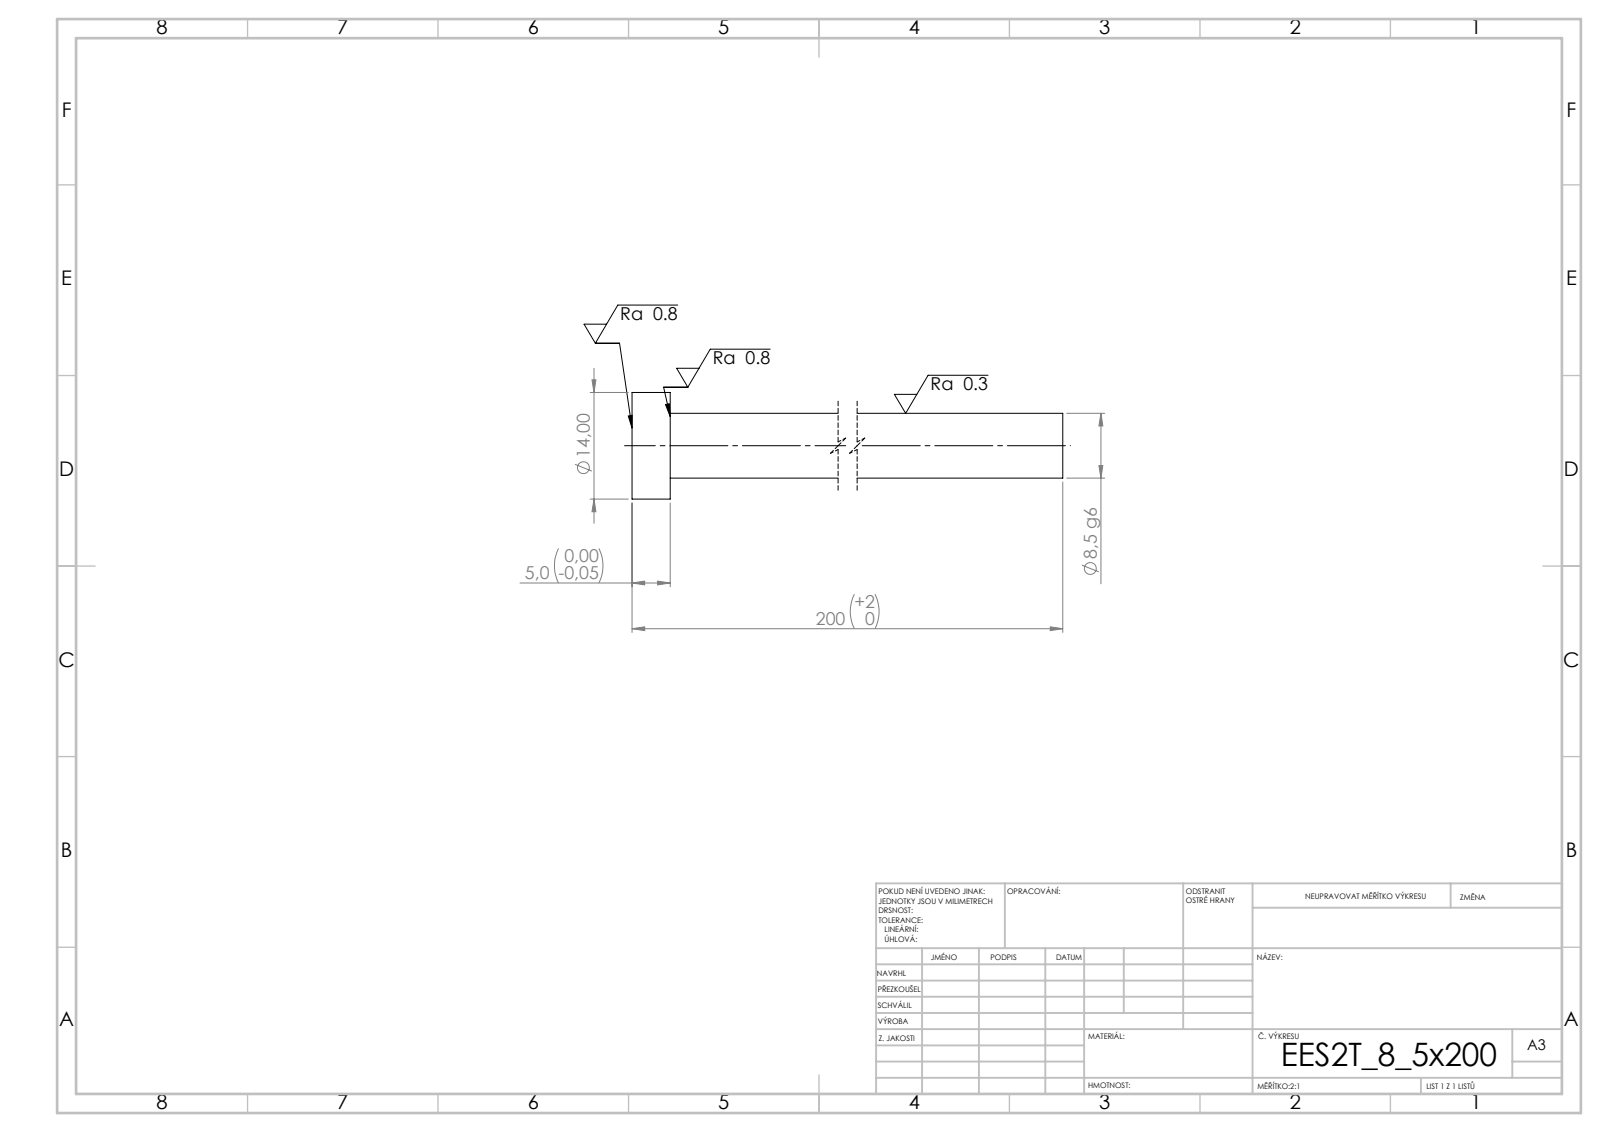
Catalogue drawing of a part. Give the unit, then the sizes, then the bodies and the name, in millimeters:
Units: millimetres
Overall size (bounding box): 200 × 14 × 14
Round bosses / shafts (diameter × count): ⌀14 ×1, ⌀8.5 ×1
Main face-to-face distances: 5, 200, 195
Volume: 11 835 mm³ · Surface area: 5 735 mm²
Bodies: 1 solid, 7 faces (3 planar, 4 cylindrical, 0 other)
STEP written by: SolidWorks 2019 (CONFIG_CONTROL_DESIGN)
